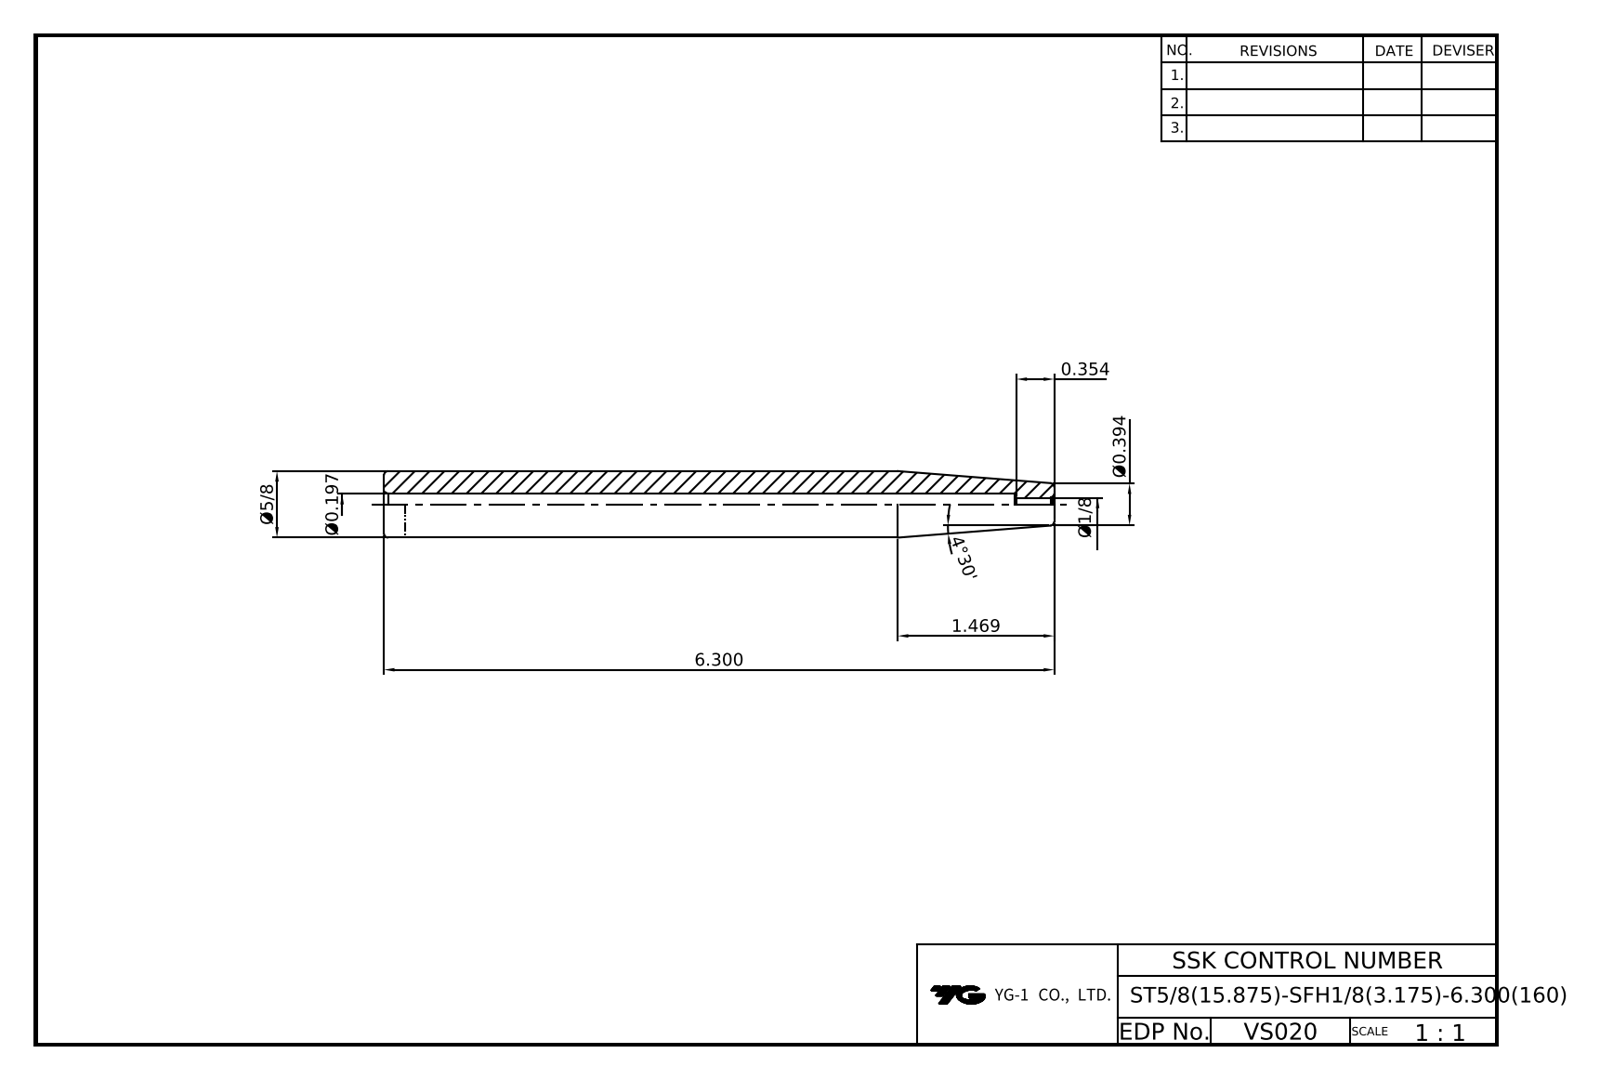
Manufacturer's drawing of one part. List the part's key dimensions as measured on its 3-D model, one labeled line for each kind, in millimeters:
Part name (STEP PRODUCT): LO-ST15.875-SFH3.175-6.30(20240115)
STEP written by: Autodesk Inventor 2024 (AUTOMOTIVE_DESIGN)
Units: millimetres
Bodies: 1 solid, 10 faces (2 planar, 3 cylindrical, 5 other)
Overall size (bounding box): 160 × 15.88 × 15.88
Volume: 26 229 mm³ · Surface area: 10 315 mm²
Round holes (diameter × count): ⌀3 ×1, ⌀5 ×1
Round bosses / shafts (diameter × count): ⌀15.87 ×1
Main face-to-face distances: 160
